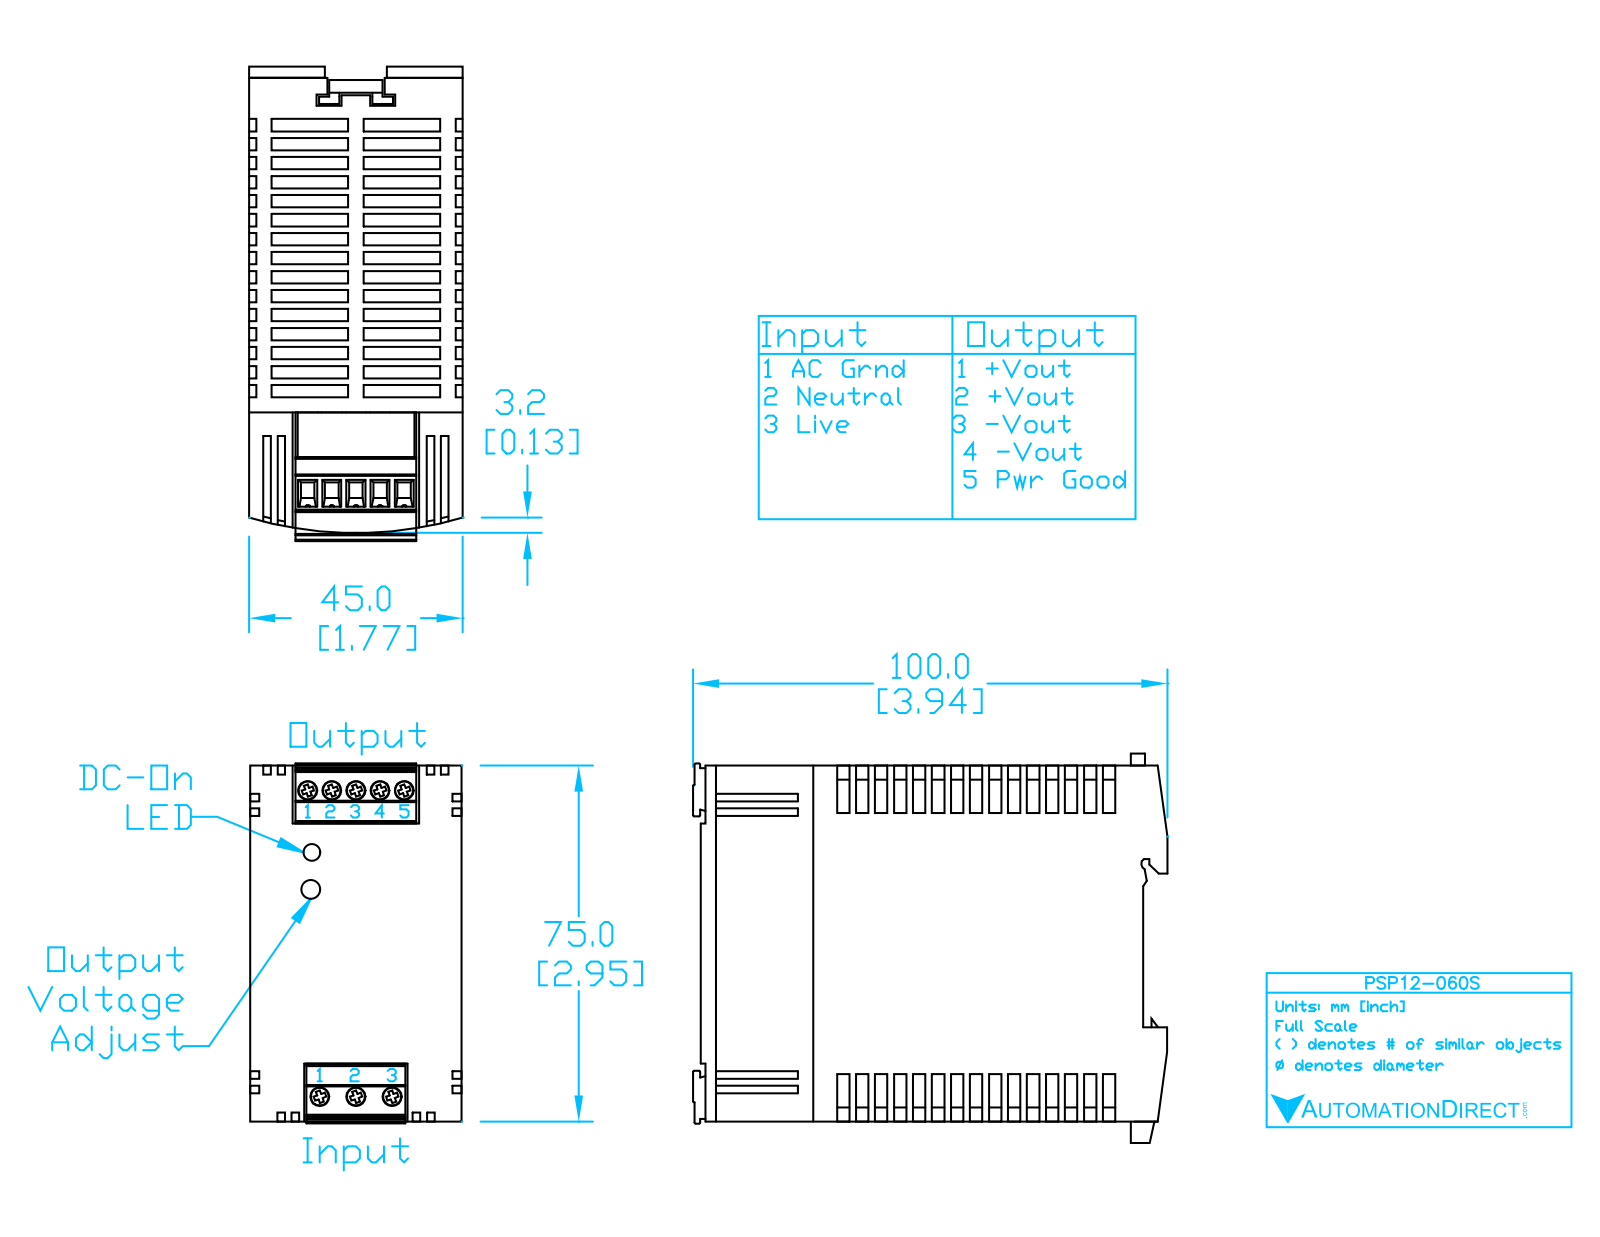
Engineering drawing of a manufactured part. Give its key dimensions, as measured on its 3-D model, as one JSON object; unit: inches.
{"part_name": "PSP12-060S", "step_written_by": "SolidWorks 2011 (CONFIG_CONTROL_DESIGN)", "units": "inches", "bodies": {"solids": 23, "faces": 341, "planar": 272, "cylindrical": 0, "other": 69}, "overall_size": [4.016, 3.15, 1.772], "volume_in3": 23.35, "surface_area_in2": 95.17, "face_to_face_distances": [1.772, 2.953, 2.711, 0.565, 2.387, 0.079, 2.789, 0.093, 0.467, 0.482]}
